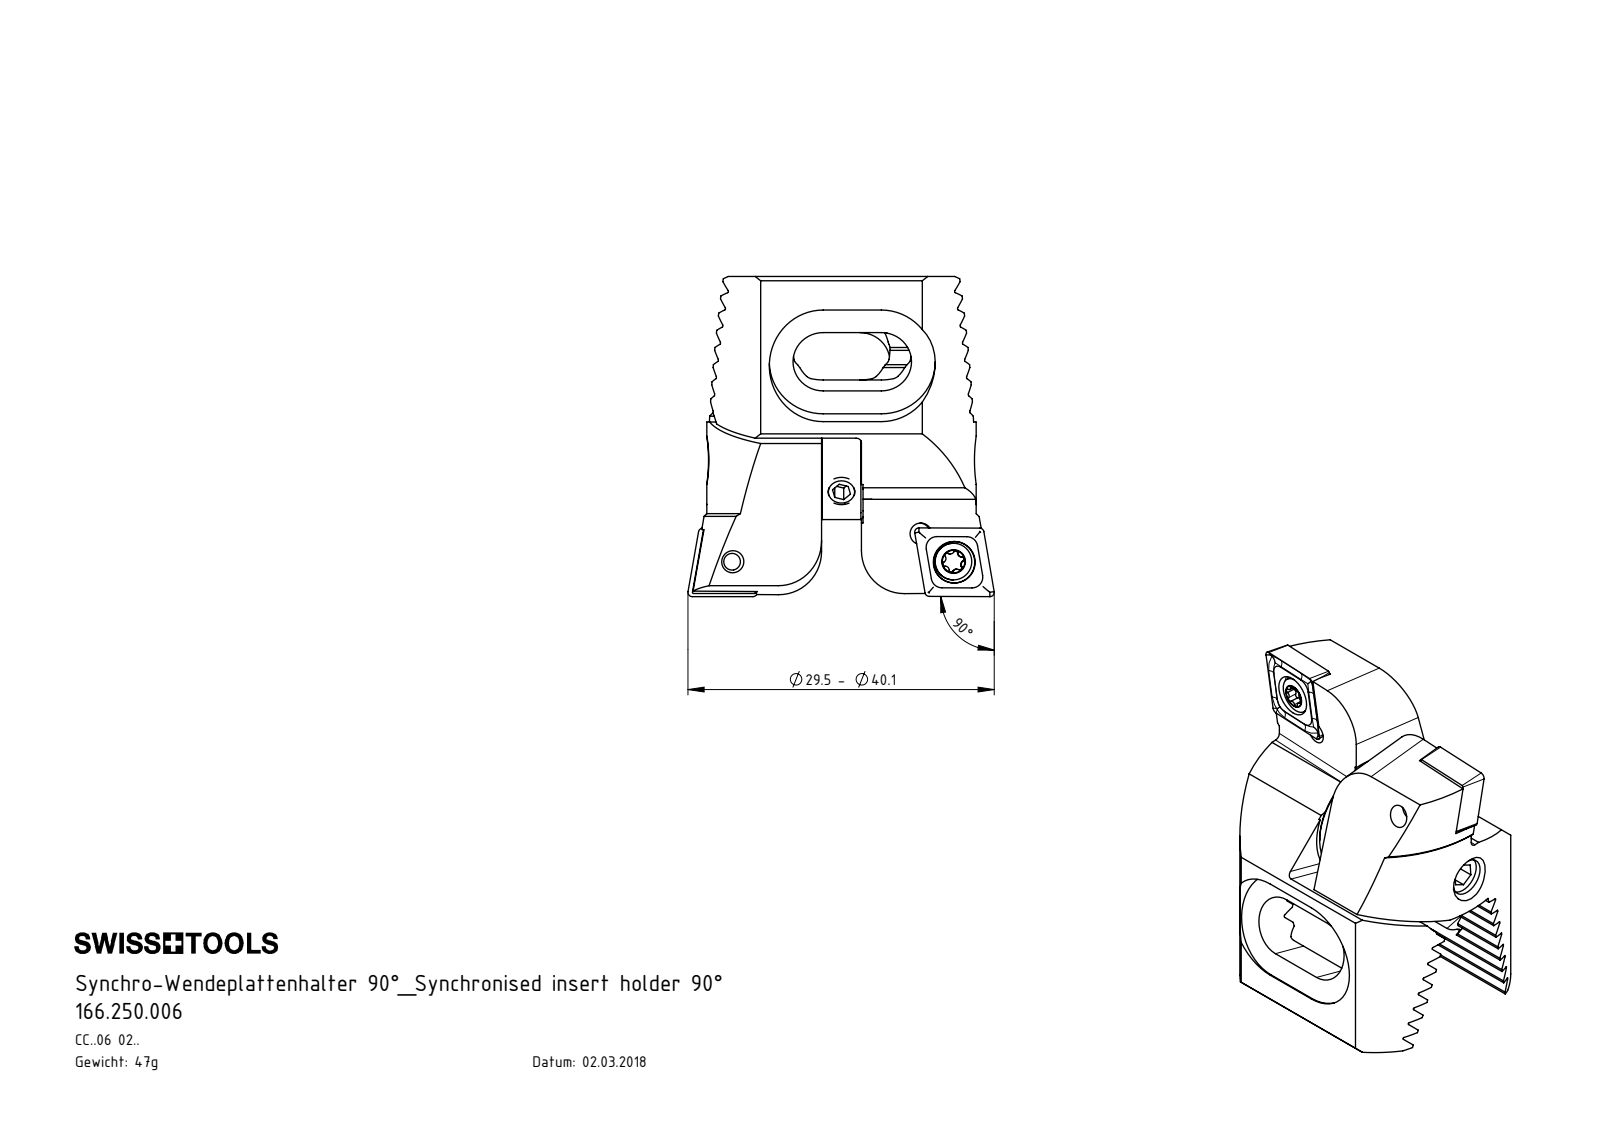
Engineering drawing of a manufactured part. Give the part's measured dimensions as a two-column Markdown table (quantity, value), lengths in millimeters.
| quantity | value |
| --- | --- |
| part name | Z25-WCA.003.016_A; Z25-WCA.001.016_A; ISO 4026 - M3 x 3; WCA-ER2.001.006_A (+4 more) |
| STEP written by | SolidWorks 2017 (CONFIG_CONTROL_DESIGN) |
| units | millimeters |
| bodies | 11 solids, 517 faces (205 planar, 172 cylindrical, 140 other) |
| overall size | 29.7 × 28.43 × 20.2 |
| volume | 5 848 mm³ |
| surface area | 5 400 mm² |
| round holes (diameter × count) | 1 × 3, 2.5 × 3, 2 × 2, 2.05 × 2, 2.8 × 2, 3.85 × 2, 3.5 × 1 |
| round bosses / shafts (diameter × count) | 3 × 4, 3.4 × 2, 2.5 × 2, 11 × 1, 4 × 1 |
| partial cylindrical surfaces (radius × count) | 0.12 × 16, 0.21 × 12, 0.36 × 10, 1 × 8, 0.5 × 4, 2.8 × 4, 5 × 4, 0.36 × 2 |
| main face-to-face distances | 1.43, 2.86, 4.29, 5.72, 3.14, 7.14, 8.57, 7.15, 4, 5.71 |
| hole center spacings | 2, 3.98, 3.99, 4.08, 4.09, 7.19, 7.2, 7.47 |
